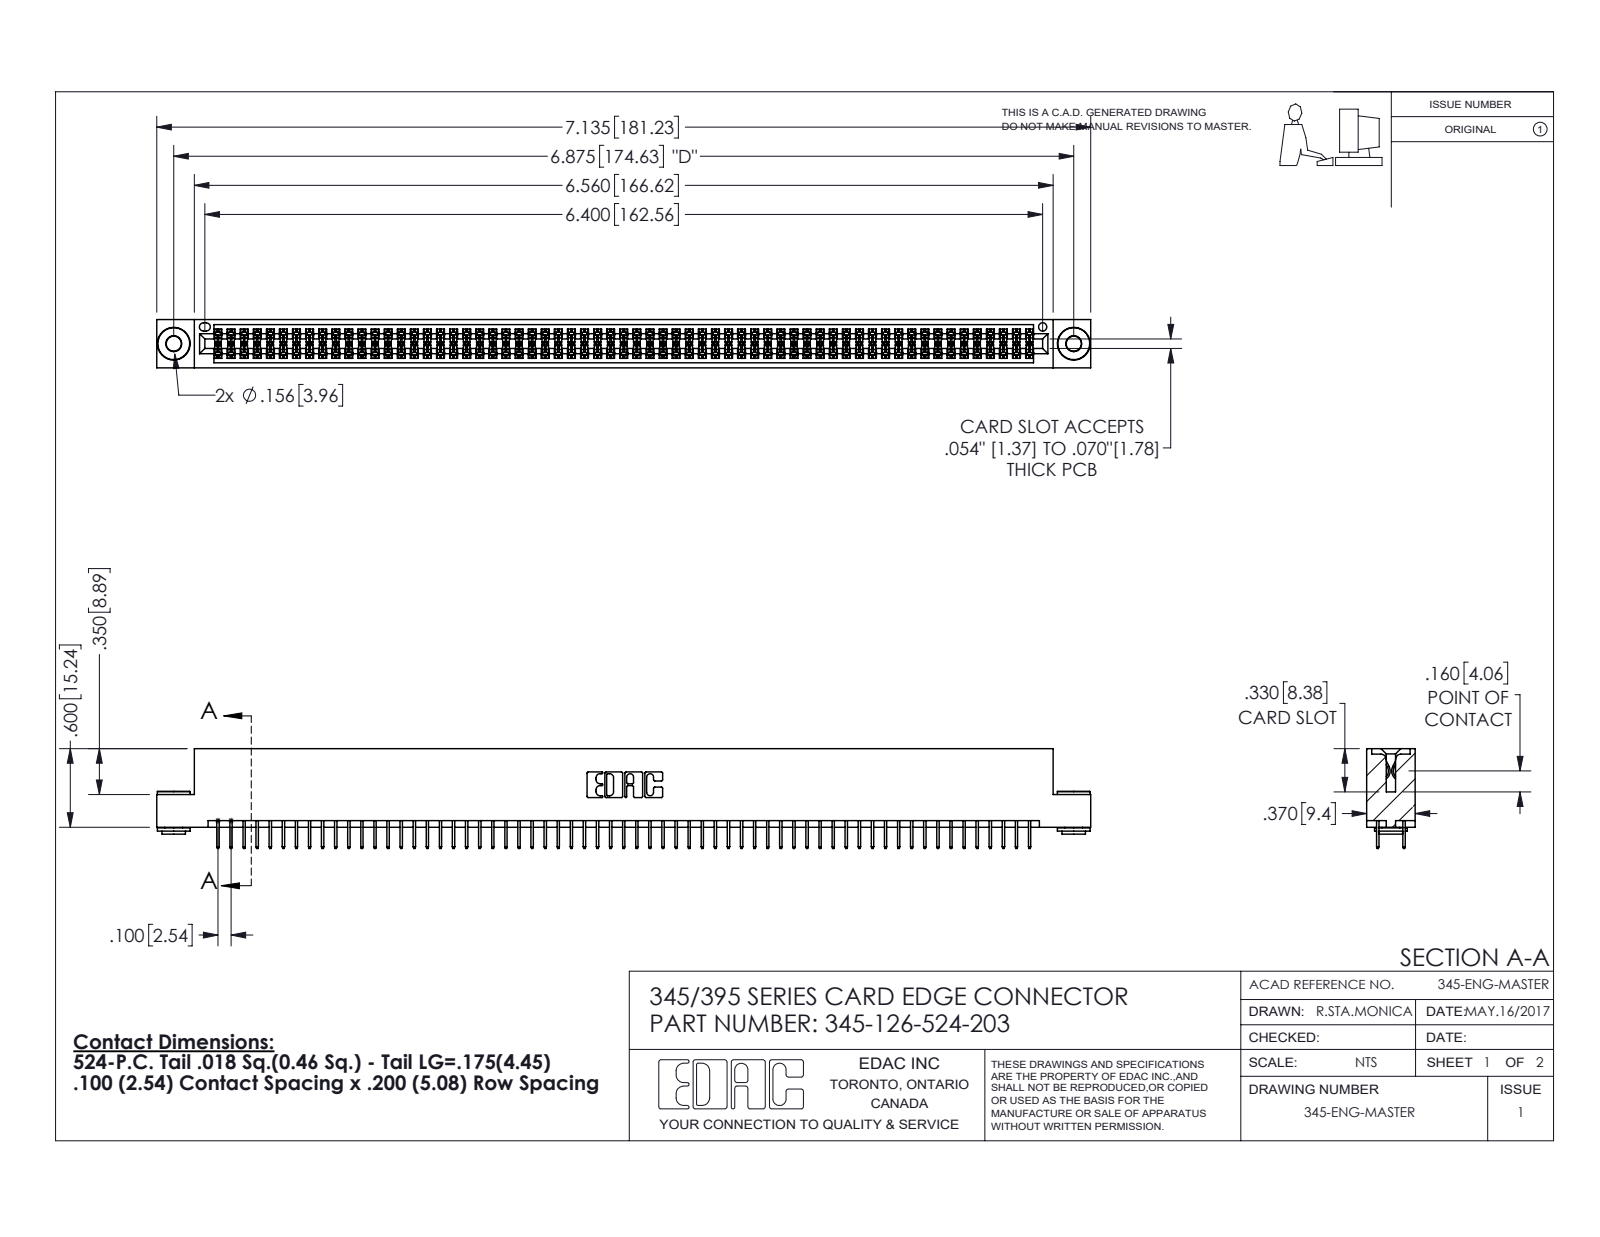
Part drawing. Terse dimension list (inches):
name: 345-250-002_345-250-002-102; 345 Part_Flush Mounting Lugs - 0.156 Dia-TH; 345-292-001_345-293-124; 345-126-524-203
written by: SolidWorks 2016 (CONFIG_CONTROL_DESIGN)
unit: in
bodies: 129 solids, 6968 faces (5004 planar, 1956 cylindrical, 8 other)
size: 7.135 × 0.762 × 0.37
volume: 1.076 in³; area: 40.56 in²
holes: 2× ⌀0.116, 2× ⌀0.156, 1× ⌀0.064
bosses: 2× ⌀0.25, 2× ⌀0.18, 2× ⌀0.136
rounds: 189× R0.006, 22× R0.01, 6× R0.007, 6× R0.031, 3× R0.026, 2× R0.014, 2× R0.019, 2× R0.022
face distances: 0.072, 0.298, 0.2, 0.37, 0.025, 0.098, 0.272, 0.225, 0.072, 0.175
hole spacings: 0.27, 6.639, 6.875
